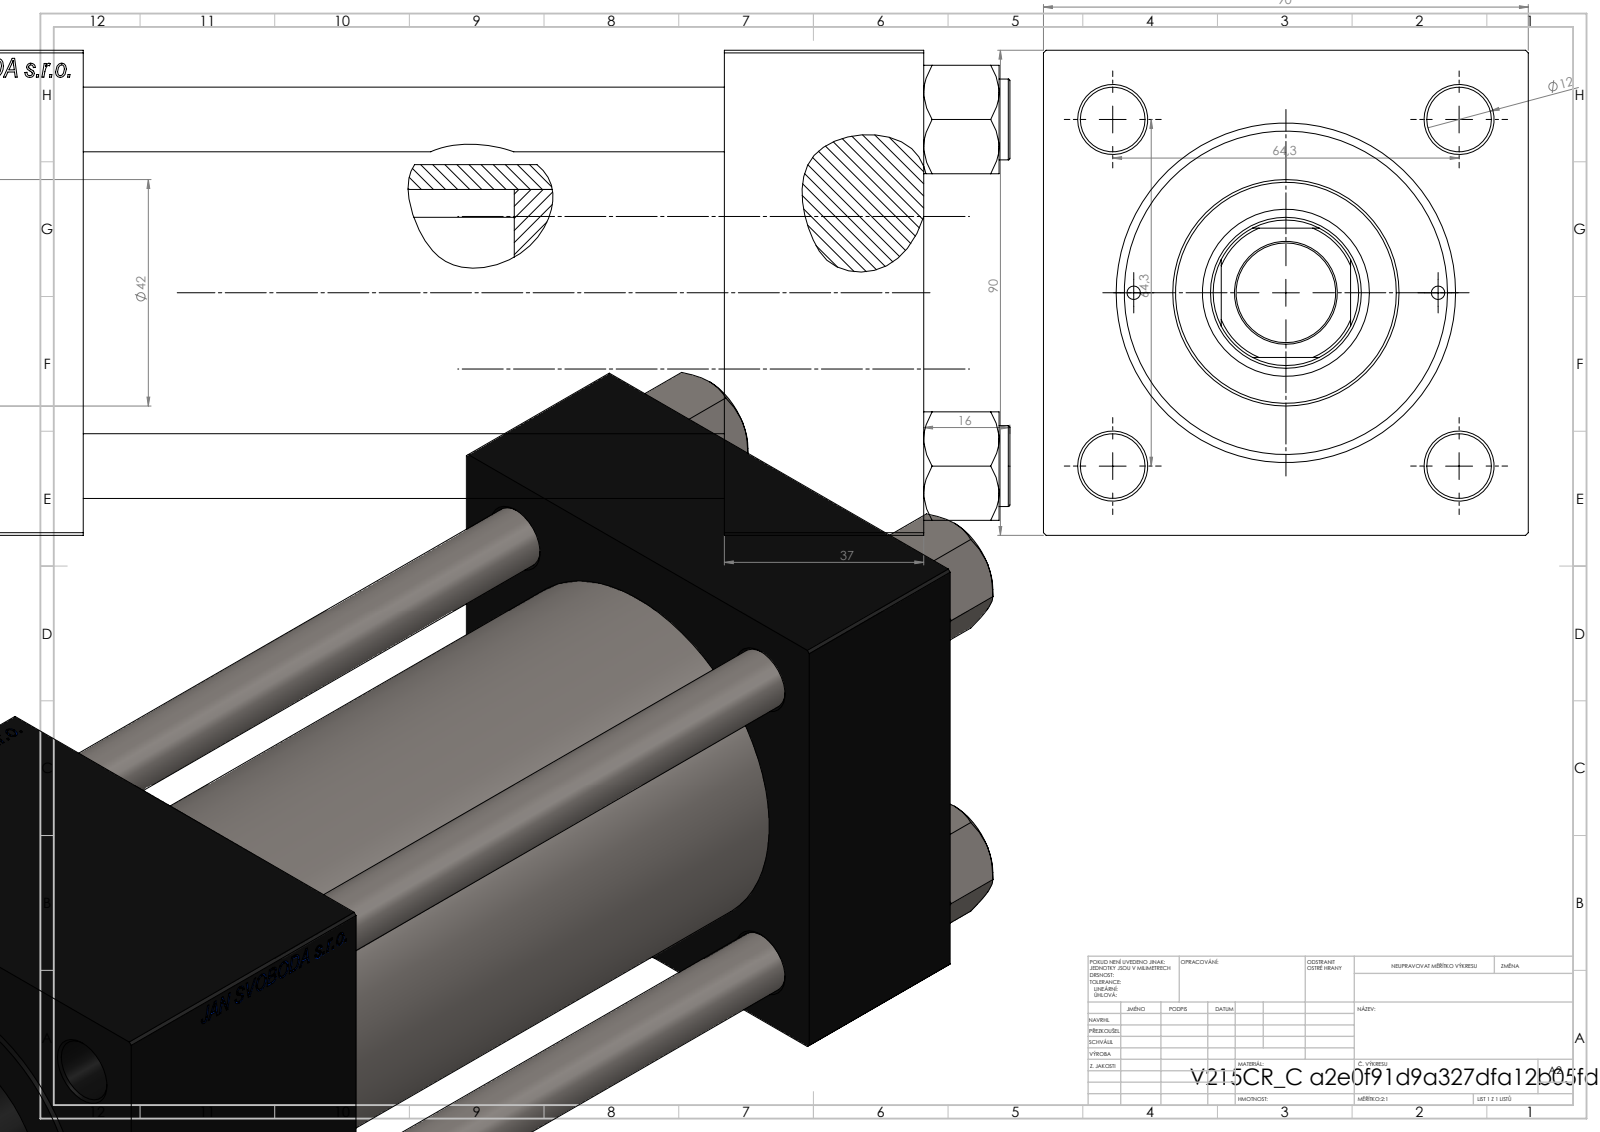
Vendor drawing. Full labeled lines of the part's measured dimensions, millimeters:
Part name (STEP PRODUCT): V215CR_C_TYCINKA; V215CR_C_Body; V215_VC_A; NUT_M5_C (+1 more)
STEP written by: SolidWorks 2019 (CONFIG_CONTROL_DESIGN)
Units: millimetres
Bodies: 11 solids, 1154 faces (528 planar, 90 cylindrical, 536 other)
Overall size (bounding box): 263 × 90 × 90
Volume: 1 048 000 mm³ · Surface area: 218 414 mm²
Round holes (diameter × count): ⌀12 ×4, ⌀2.5 ×2, ⌀7 ×2, ⌀20.96 ×2, ⌀30 ×2, ⌀18.5 ×1, ⌀28 ×1, ⌀31 ×1, ⌀50 ×1, ⌀60 ×1, ⌀63 ×1
Round bosses / shafts (diameter × count): ⌀15 ×4, ⌀69 ×1, ⌀42 ×1
Partial cylindrical surfaces — rounded edges, fillets, slot ends (radius × count): R13.5 ×1
Main face-to-face distances: 90, 37, 215, 178, 156, 119, 59, 186.3, 149.3, 30.3
Hole centre spacings: 32.39, 45.47, 64.3, 68.42, 28.25, 90.93, 56.5, 157.5
